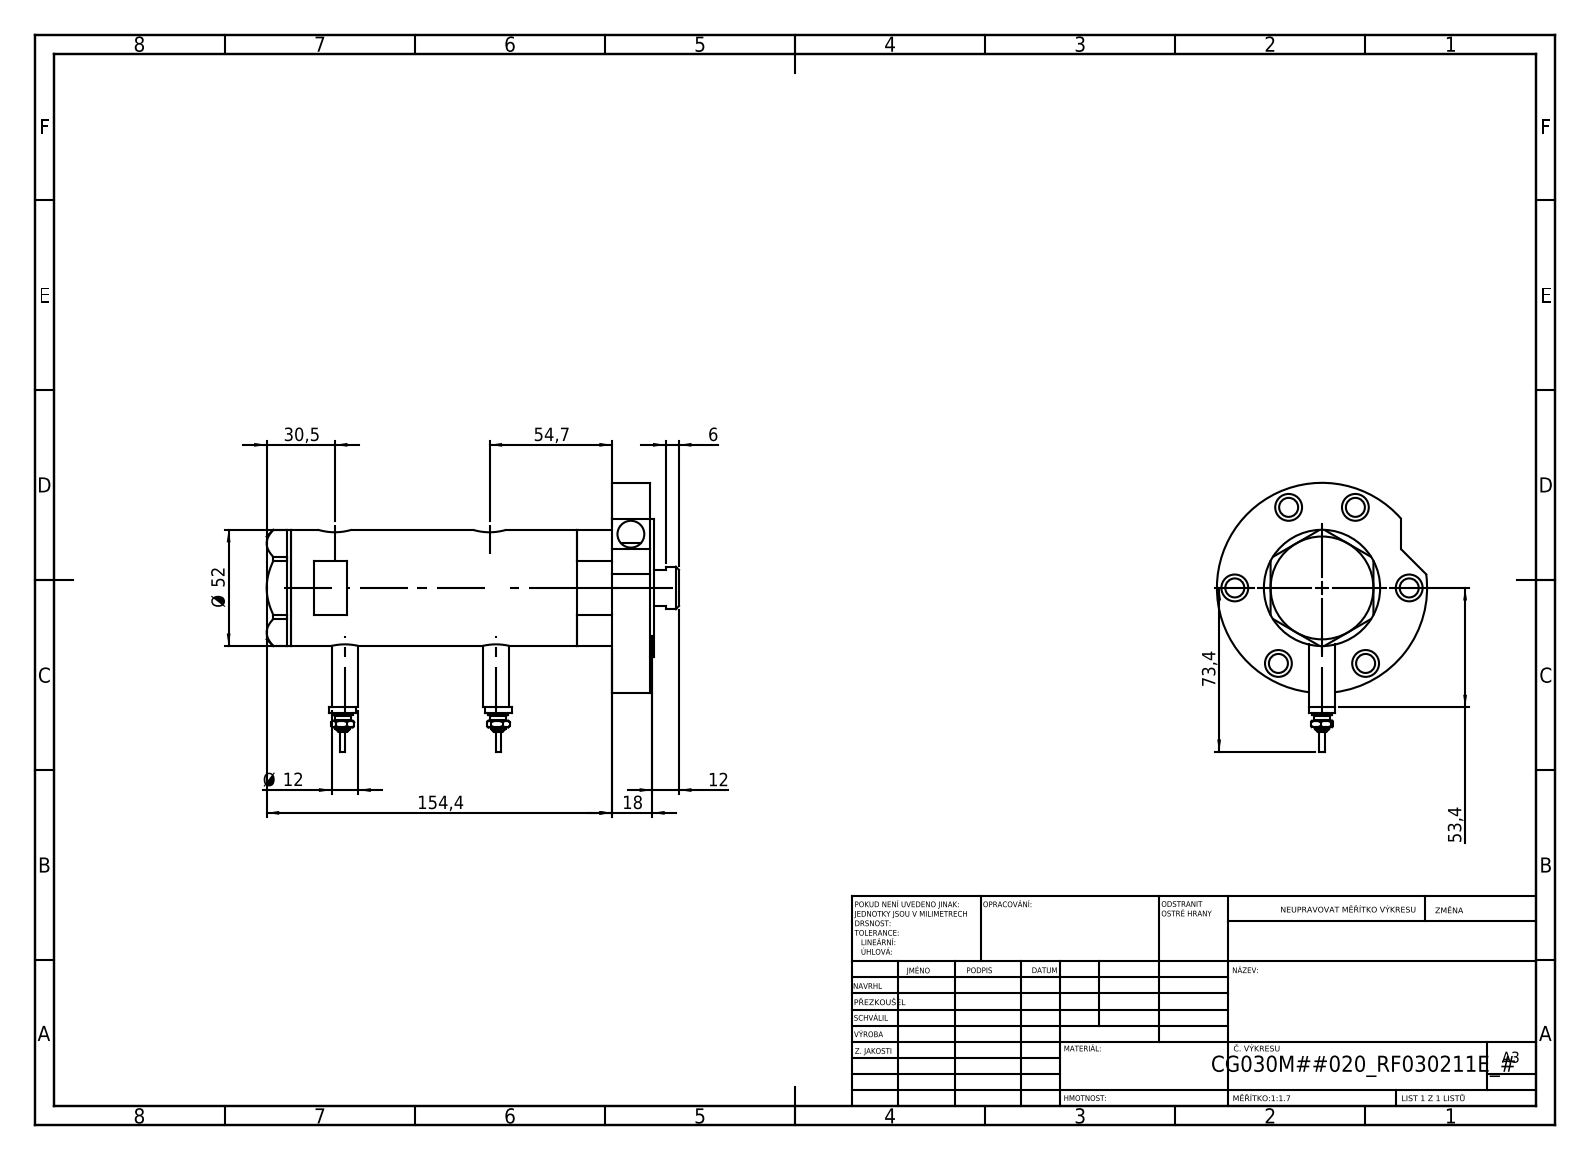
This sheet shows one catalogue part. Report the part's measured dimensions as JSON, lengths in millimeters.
{"part_name": "V270CG_VC; Switch; V270CG_RF211E; V270CG_FRONT (+2 more)", "step_written_by": "SolidWorks 2019 (CONFIG_CONTROL_DESIGN)", "units": "millimeters", "bodies": {"solids": 7, "faces": 270, "planar": 104, "cylindrical": 102, "other": 64}, "overall_size": [184.4, 120.4, 94], "volume_mm3": 426673, "surface_area_mm2": 104009, "round_holes": [[12, 7], [8.5, 6], [9.73, 2], [12.5, 2], [15, 2], [6.5, 1], [20, 1], [21.5, 1], [30, 1], [33, 1], [40, 1], [44, 1]], "round_bosses_or_shafts": [[12, 4], [9, 2], [7, 2], [4.5, 2], [2.5, 2], [94, 1], [62, 1], [52, 1]], "face_to_face_distances": [17, 143.4, 160.4, 2, 162.4, 91.5, 51.9, 68.9, 11, 173.4], "hole_center_spacings": [39, 43.34, 64.85, 67.55, 69.95, 77.83, 2.9, 4.5]}
